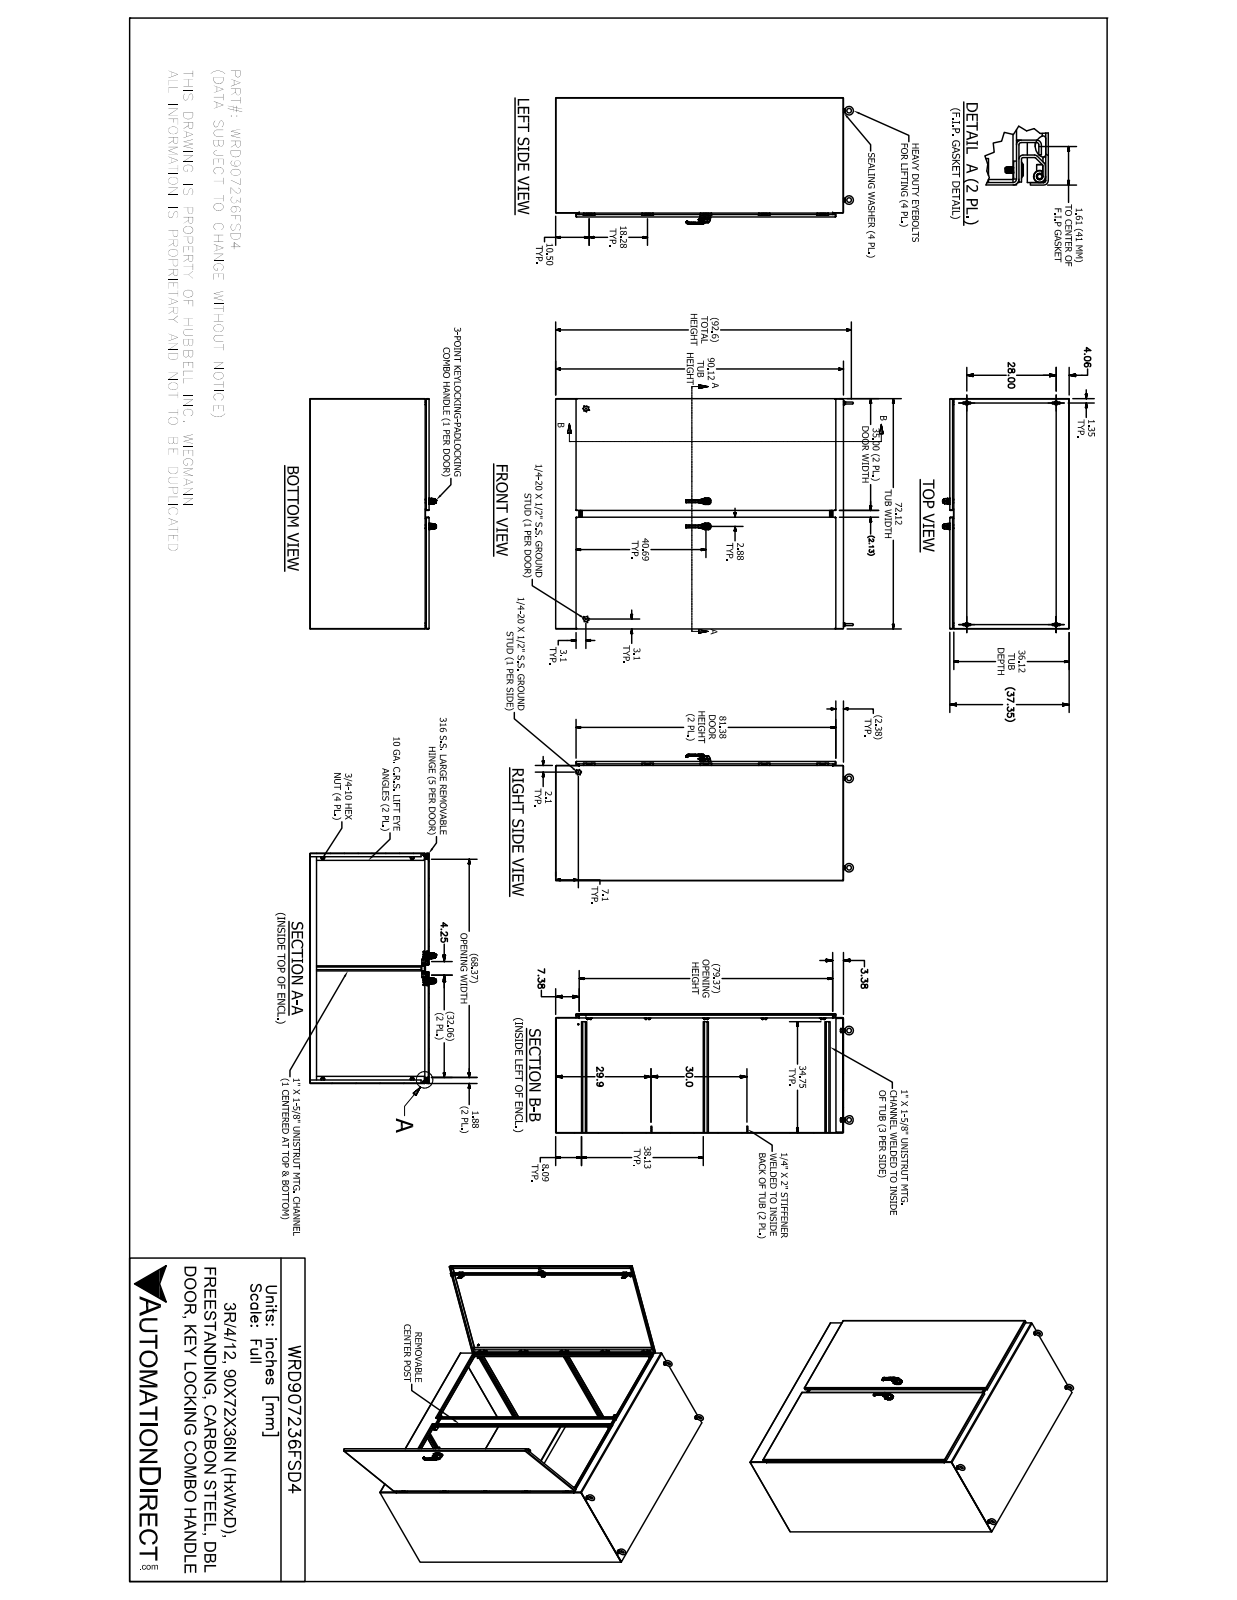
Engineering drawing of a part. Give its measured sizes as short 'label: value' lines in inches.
name: WRD907236FSD4
written by: SolidWorks 2017 (AUTOMOTIVE_DESIGN)
unit: in
bodies: 177 solids, 3716 faces (1682 planar, 1220 cylindrical, 814 other)
size: 93.248 × 72.133 × 39.527
volume: 3 187 in³; area: 58 773 in²
holes: 24× ⌀0.266, 20× ⌀0.23, 20× ⌀0.281, 20× ⌀0.65, 8× ⌀0.2, 8× ⌀0.277, 6× ⌀0.281, 4× ⌀0.156, 4× ⌀0.252, 4× ⌀0.4, 4× ⌀0.45, 4× ⌀0.642
bosses: 14× ⌀0.25, 13× ⌀0.625, 7× ⌀0.625, 4× ⌀1.25, 4× ⌀1.12, 4× ⌀0.75, 4× ⌀0.533, 4× ⌀0.438
rounds: 56× R0.062, 36× R0.125, 32× R0.05, 20× R0.01, 16× R0.019, 16× R0.025, 16× R0.053, 16× R0.063
face distances: 0.104, 37.245, 72.021, 37.141, 37.349, 90.021, 71.917, 72.125, 89.917, 36.021
hole spacings: 73.195, 18.281, 1, 70.875, 70.882, 36.563, 54.844, 72.952
